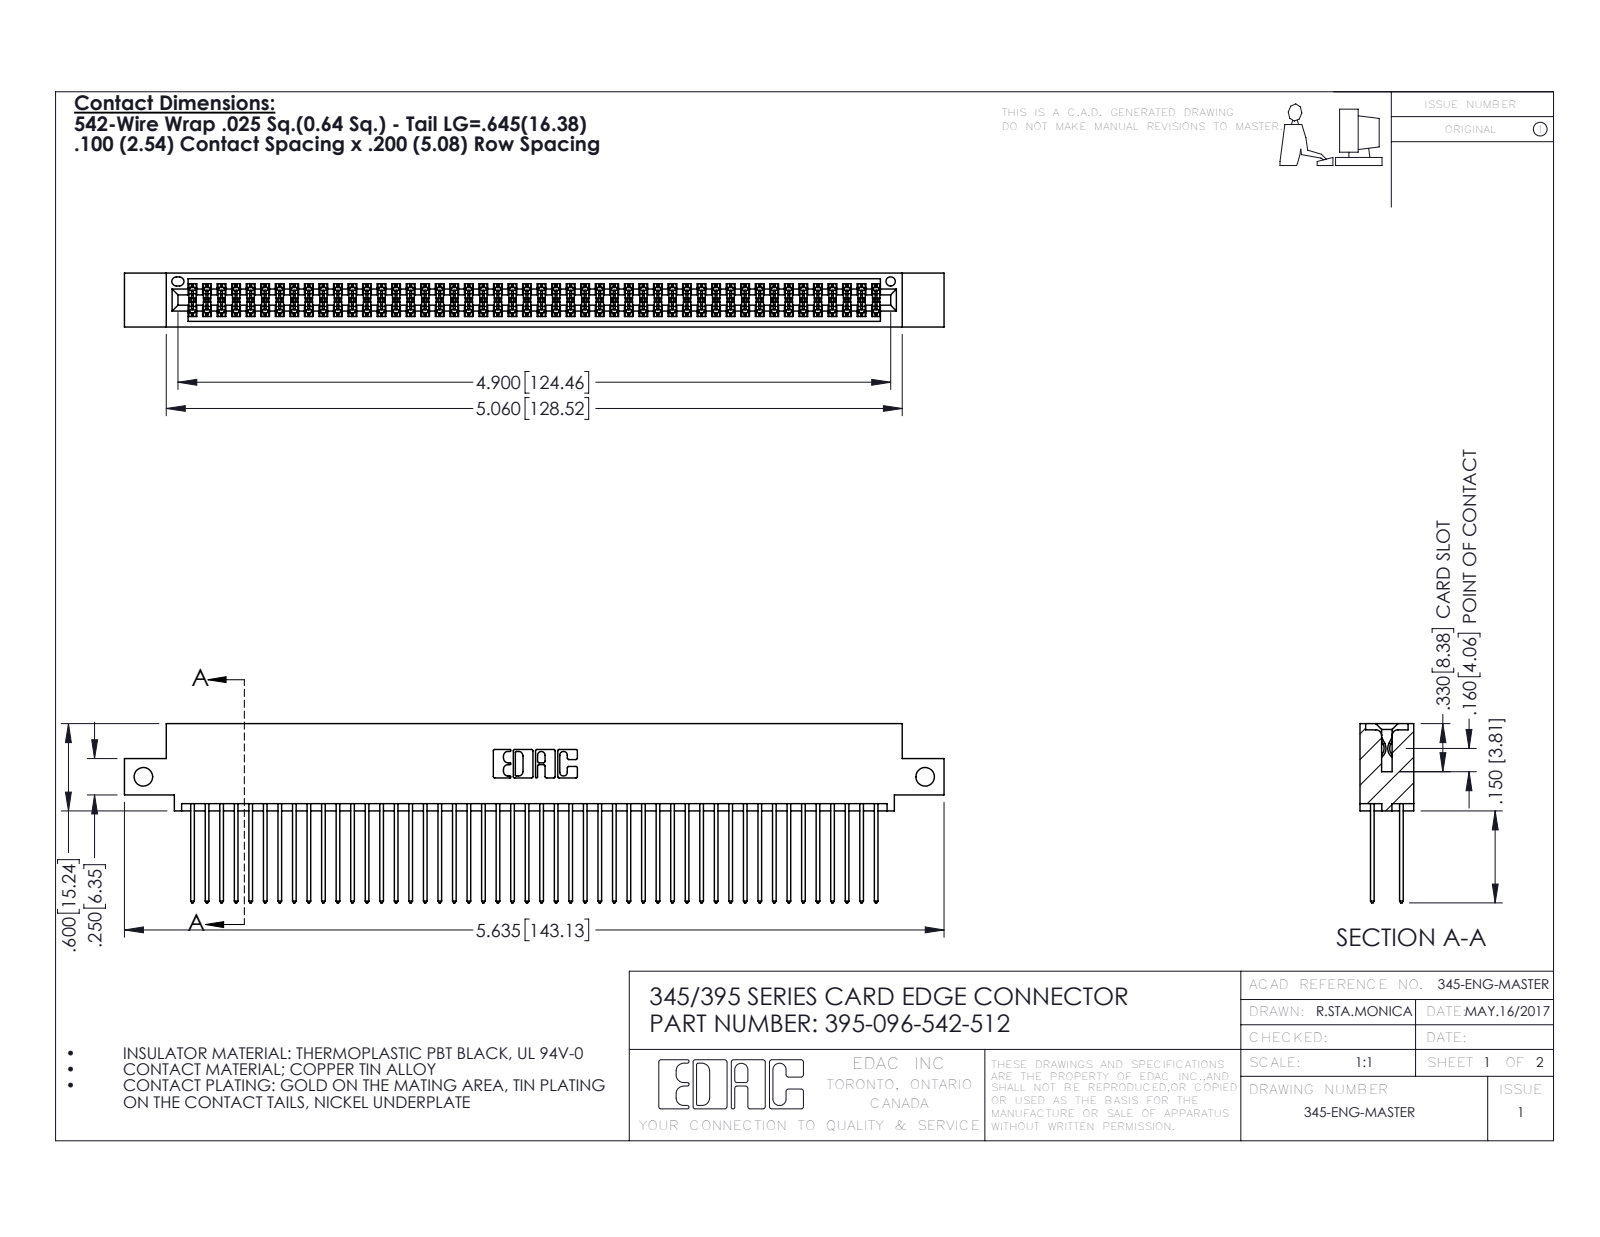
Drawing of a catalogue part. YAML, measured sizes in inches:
part_name: "395-096-542-512; 345-292-001_345-293-142; 345 Part_0.110 Offset - Side Mount"
step_written_by: "SolidWorks 2016 (CONFIG_CONTROL_DESIGN)"
units: inches
bodies: {solids: 97, faces: 4930, planar: 3252, cylindrical: 1678, other: 0}
overall_size: [5.635, 1.232, 0.37]
volume: 0.869
surface_area: 36
round_holes:
  - {diameter: 0.128, count: 2}
  - {diameter: 0.064, count: 1}
partial_cylinders:
  - {radius: 0.006, count: 144}
  - {radius: 0.01, count: 96}
  - {radius: 0.01, count: 22}
  - {radius: 0.007, count: 6}
  - {radius: 0.031, count: 6}
  - {radius: 0.026, count: 3}
  - {radius: 0.014, count: 2}
  - {radius: 0.019, count: 2}
face_to_face_distances: [0.298, 0.072, 0.2, 0.098, 0.272, 0.025, 0.225, 0.37, 0.175, 0.149]
hole_center_spacings: [5.375]
